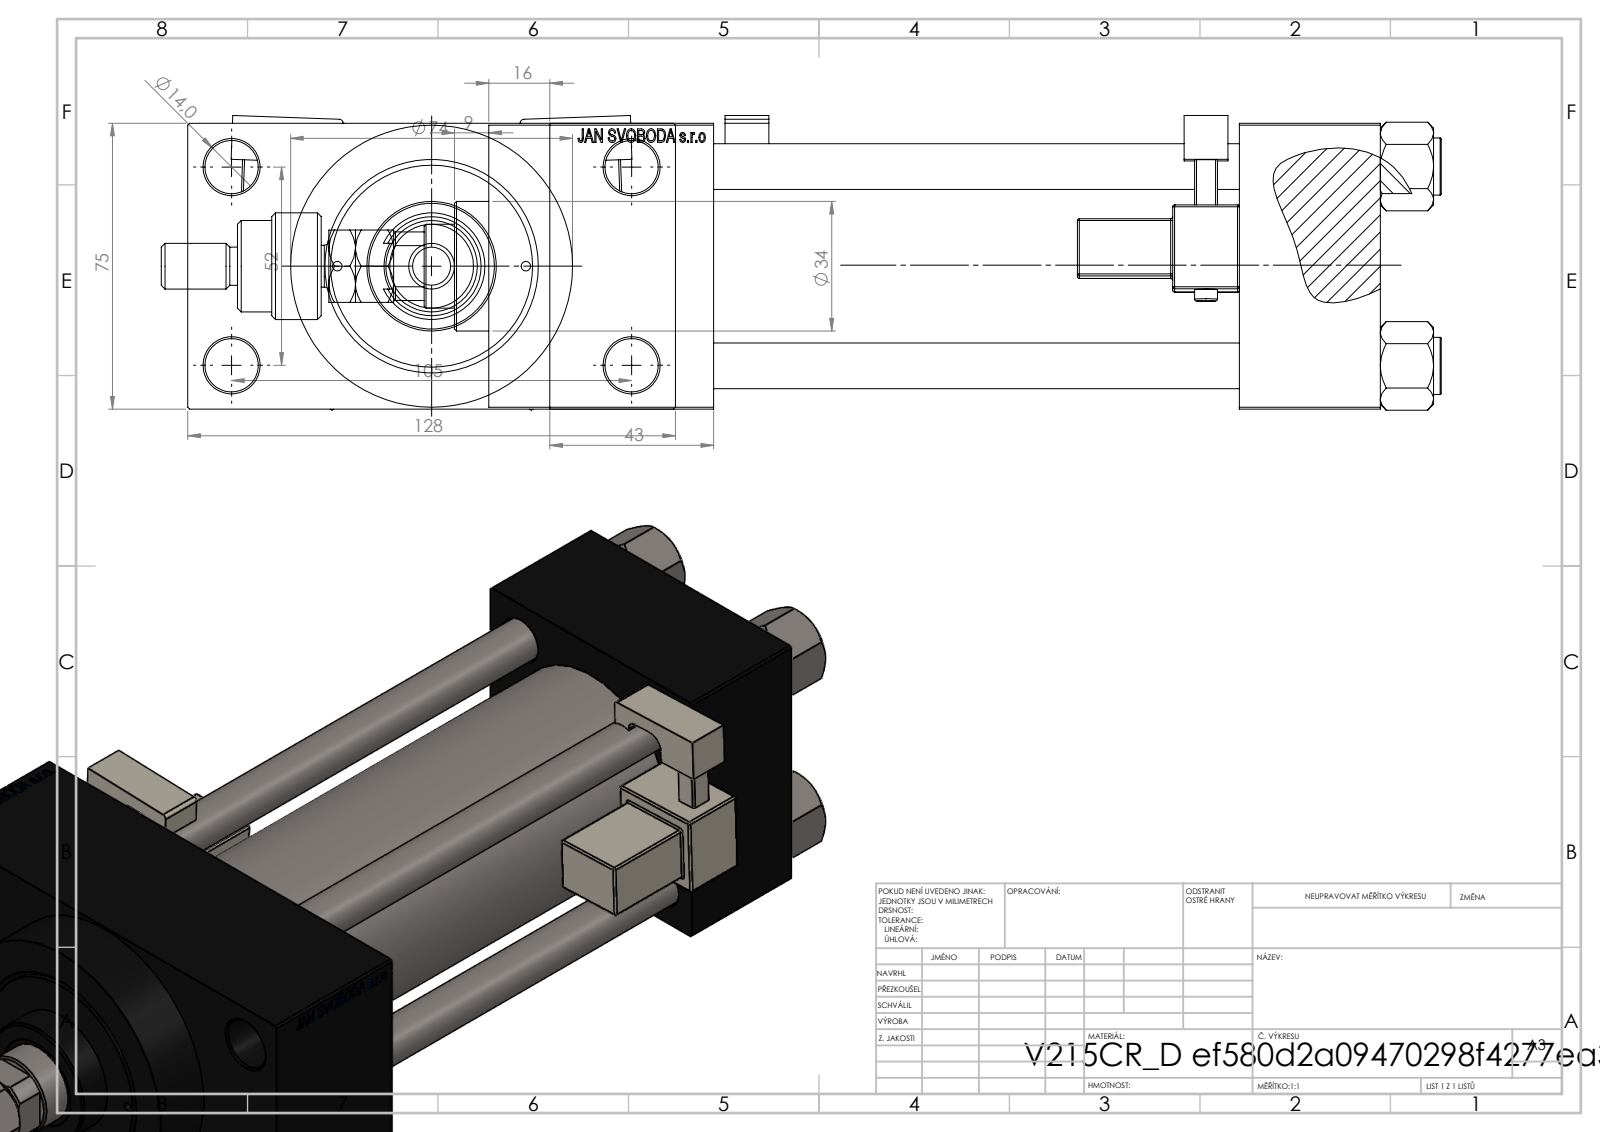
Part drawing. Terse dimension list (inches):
name: V215_VC_A; V215CR_MSU; FEMALE_PART_FOR_DFA; V215CR_VCP_D (+4 more)
written by: SolidWorks 2019 (CONFIG_CONTROL_DESIGN)
unit: in
bodies: 15 solids, 1350 faces (585 planar, 165 cylindrical, 600 other)
size: 13.228 × 5.039 × 3.043
volume: 58.76 in³; area: 356.9 in²
holes: 4× ⌀0.472, 4× ⌀0.551, 2× ⌀0.098, 2× ⌀0.276, 2× ⌀0.825, 2× ⌀1.181, 1× ⌀0.413, 1× ⌀0.866, 1× ⌀0.984, 1× ⌀1.614, 1× ⌀1.969, 1× ⌀2.087
bosses: 4× ⌀0.591, 2× ⌀0.236, 1× ⌀2.913, 1× ⌀2.205, 1× ⌀1.339, 1× ⌀1.102, 1× ⌀0.945, 1× ⌀0.709
rounds: 48× R0.02, 2× R0.039, 2× R0.098, 2× R0.157, 1× R0.384, 1× R0.413
face distances: 2.953, 5.433, 1.457, 6.89, 1.043, 3.996, 8.583, 7.126, 1.693, 0.63
hole spacings: 1.031, 1.037, 1.456, 1.497, 2.059, 2.253, 2.3, 2.307
